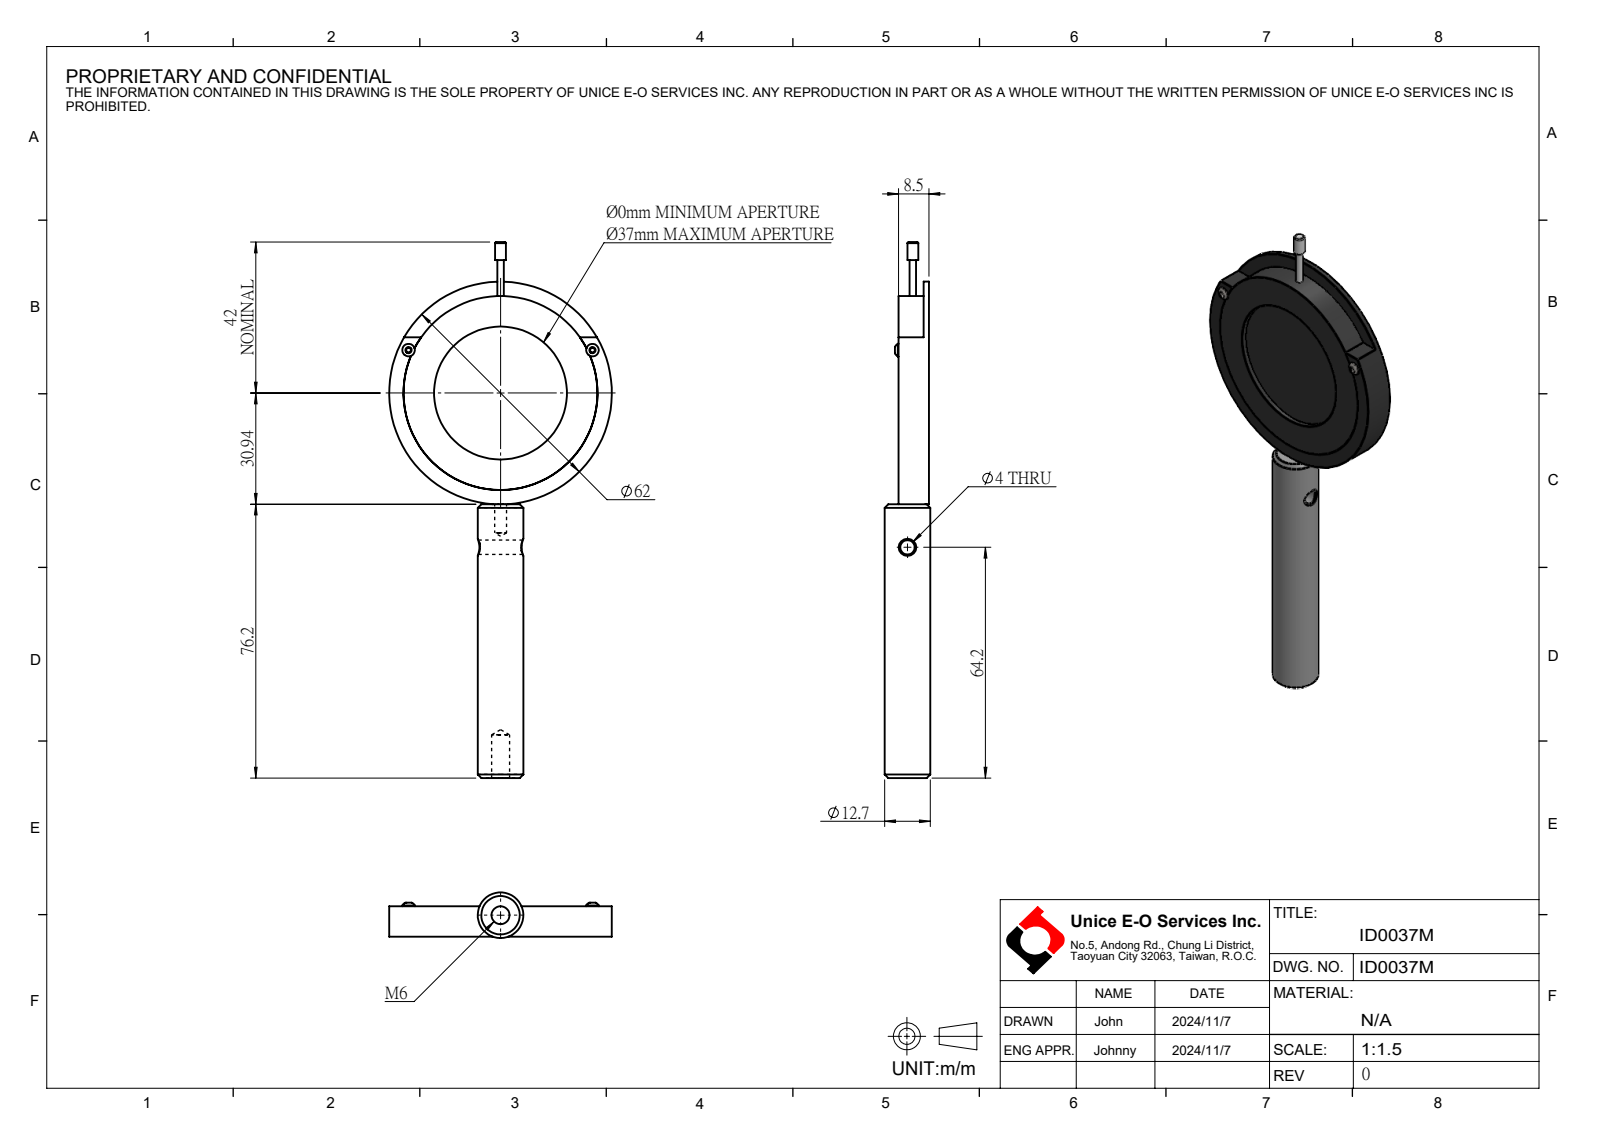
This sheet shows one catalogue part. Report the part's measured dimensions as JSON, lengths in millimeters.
{"part_name": "ID0037M", "step_written_by": "SolidWorks 2022 (CONFIG_CONTROL_DESIGN)", "units": "millimeters", "bodies": {"solids": 5, "faces": 65, "planar": 36, "cylindrical": 19, "other": 10}, "overall_size": [146.74, 62, 12.7], "volume_mm3": 28045, "surface_area_mm2": 14591, "round_holes": [[1.6, 2], [3.3, 1], [4, 1], [5, 1], [37, 1], [50, 1], [54, 1]], "round_bosses_or_shafts": [[2, 3], [3.5, 2], [62, 1], [12.7, 1], [3, 1]], "face_to_face_distances": [1.5, 6, 7.5, 1, 7, 4.5, 2.5, 8.5, 0.5, 5.5], "hole_center_spacings": [28.25, 51.2]}
